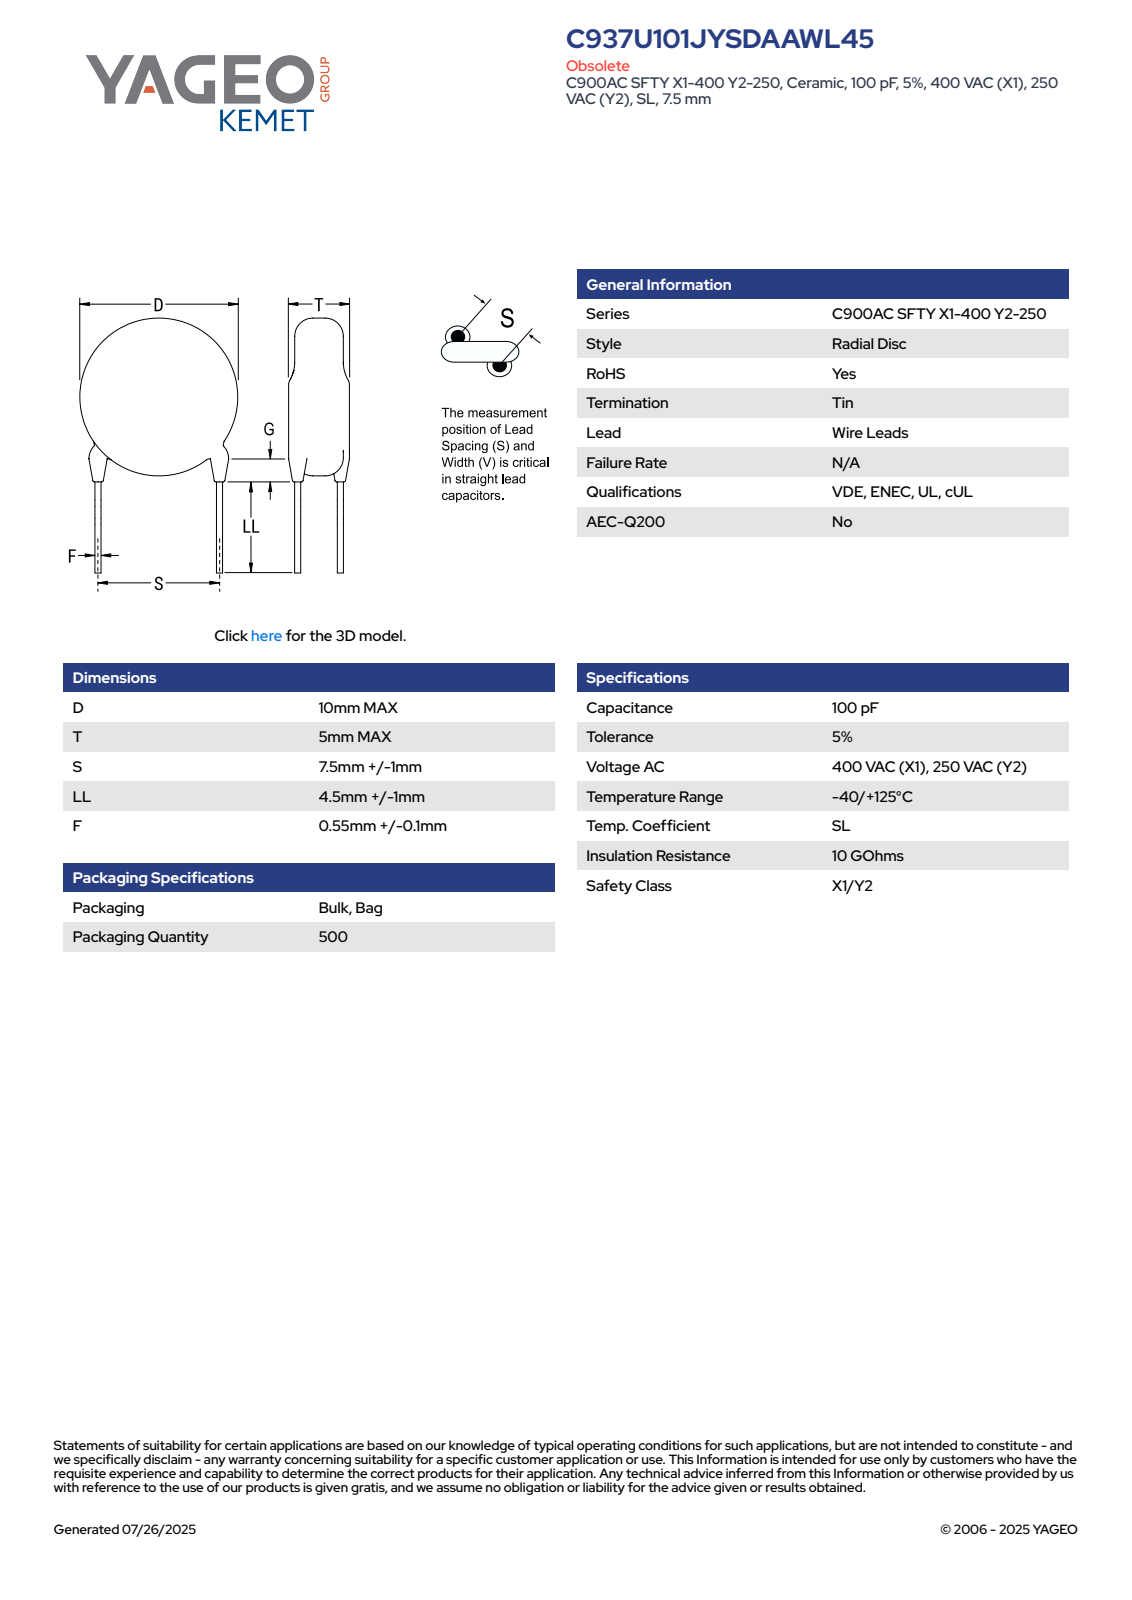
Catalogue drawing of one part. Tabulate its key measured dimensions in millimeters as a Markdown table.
| quantity | value |
| --- | --- |
| part name | CCD_STC900_D10T5S7.5LL5.5F0.65G3 |
| STEP written by | SolidWorks 2014 (AUTOMOTIVE_DESIGN) |
| units | millimeters |
| bodies | 4 solids, 83 faces (61 planar, 6 cylindrical, 16 other) |
| overall size | 15.78 × 10 × 5 |
| volume | 386 mm³ |
| surface area | 324 mm² |
| round bosses / shafts (diameter × count) | 0.65 × 2, 10 × 1 |
| main face-to-face distances | 5, 11.35, 10.2, 1.15, 0.93, 0.42, 0.31, 3.43, 3.56, 1.89 |
